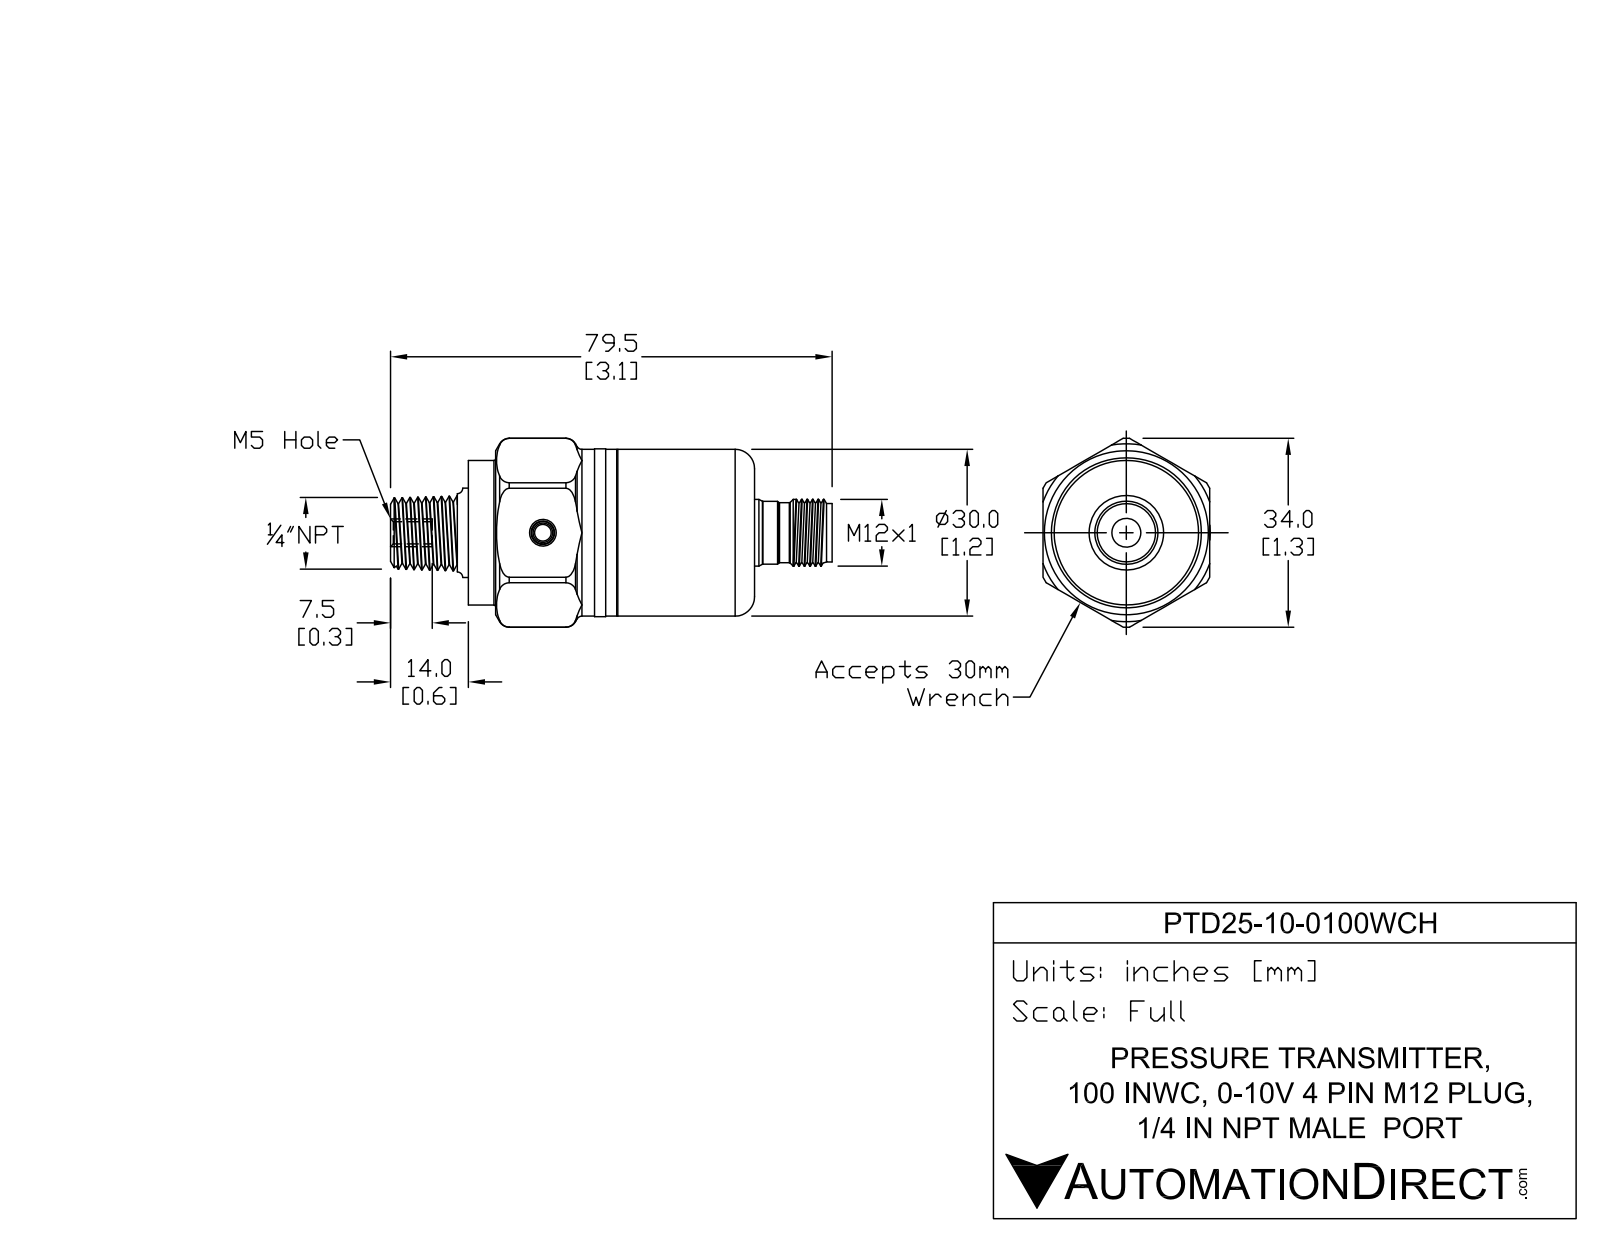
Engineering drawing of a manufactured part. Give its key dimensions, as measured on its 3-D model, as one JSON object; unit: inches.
{"part_name": "PTD25-10-0100WCH", "step_written_by": "SolidWorks 2017 (AUTOMOTIVE_DESIGN)", "units": "inches", "bodies": {"solids": 1, "faces": 124, "planar": 36, "cylindrical": 59, "other": 29}, "overall_size": [3.13, 1.33, 1.248], "volume_in3": 2.393, "surface_area_in2": 12.54, "round_holes": [[0.157, 1], [0.335, 1]], "round_bosses_or_shafts": [[1.183, 1], [1.181, 1], [1.022, 1], [0.551, 1], [0.531, 1], [0.472, 1]], "partial_cylinders_radius": [[0.148, 1], [0.667, 1]], "face_to_face_distances": [2.008, 1.18, 1.181, 1.89, 0.118, 2.559, 0.669, 0.551, 1.181, 0.222]}
